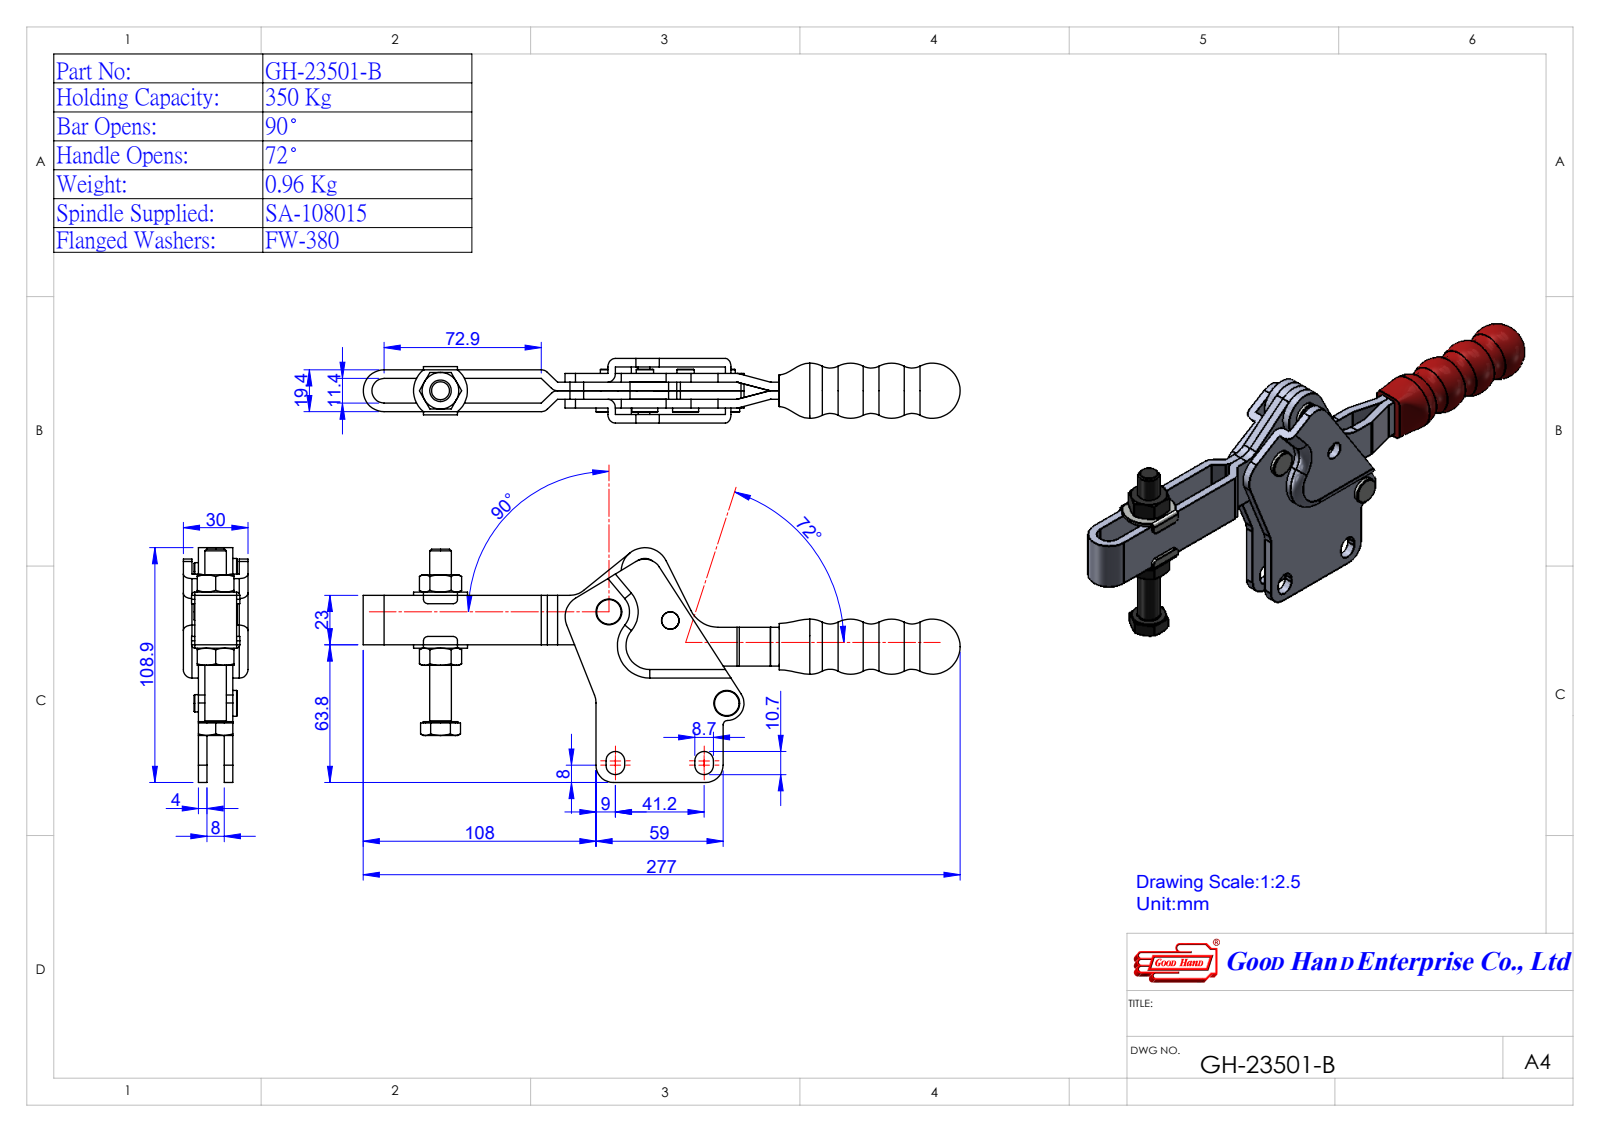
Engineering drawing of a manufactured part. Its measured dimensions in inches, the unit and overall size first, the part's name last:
Units: inches
Overall size (bounding box): 10.905 × 4.287 × 1.181
Round holes (diameter × count): ⌀0.236 ×4, ⌀0.315 ×2
Round bosses / shafts (diameter × count): ⌀0.472 ×4, ⌀0.315 ×4, ⌀0.63 ×1, ⌀0.394 ×1
Partial cylindrical surfaces — rounded edges, fillets, slot ends (radius × count): R0.079 ×8, R0.059 ×4, R0.158 ×4, R0.161 ×4, R0.171 ×4, R0.315 ×4, R0.394 ×3, R0.433 ×2
Main face-to-face distances: 0.157, 0.315, 0.472, 0.067, 0.224, 0.382, 0.539, 0.209, 0.276, 0.433
Hole centre spacings: 1.011, 1.83, 0.489, 0.489, 0.99, 1.133, 1.133, 1.341
Volume: 9.156 in³ · Surface area: 111.2 in²
Bodies: 5 solids, 390 faces (154 planar, 164 cylindrical, 72 other)
Part name (STEP PRODUCT): GH-23501-B(簡化); Group2^GH-23501-B(簡化); Group3^GH-23501-B(簡化); Group1^GH-23501-B(簡化) (+2 more)
STEP written by: SolidWorks 2016 (AUTOMOTIVE_DESIGN)
